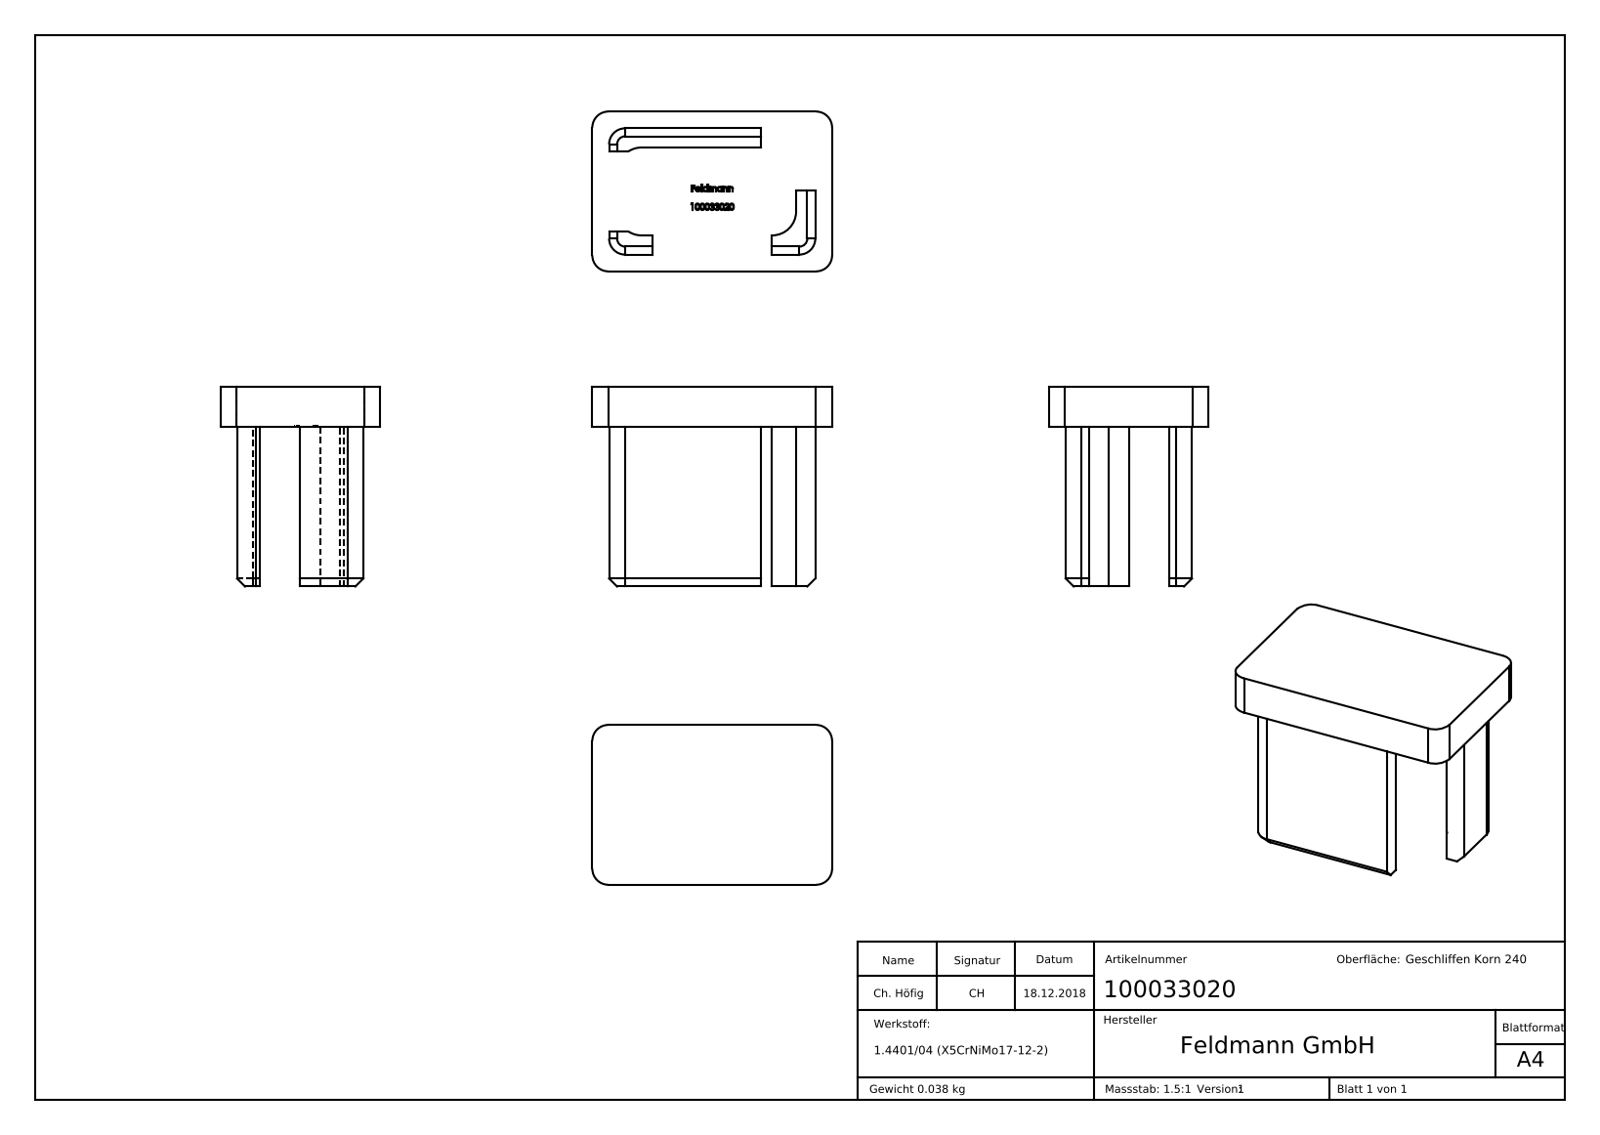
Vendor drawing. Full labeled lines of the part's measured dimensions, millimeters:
Part name (STEP PRODUCT): 100033020
STEP written by: SolidWorks 2015 (CONFIG_CONTROL_DESIGN)
Units: millimetres
Bodies: 1 solid, 267 faces (127 planar, 10 cylindrical, 130 other)
Overall size (bounding box): 30 × 25 × 20
Volume: 4 708 mm³ · Surface area: 3 305 mm²
Partial cylindrical surfaces — rounded edges, fillets, slot ends (radius × count): R2 ×7, R3 ×3
Main face-to-face distances: 5, 2.4, 2.1, 17.9, 4.5, 20, 15.5, 13.4, 15, 5.4
